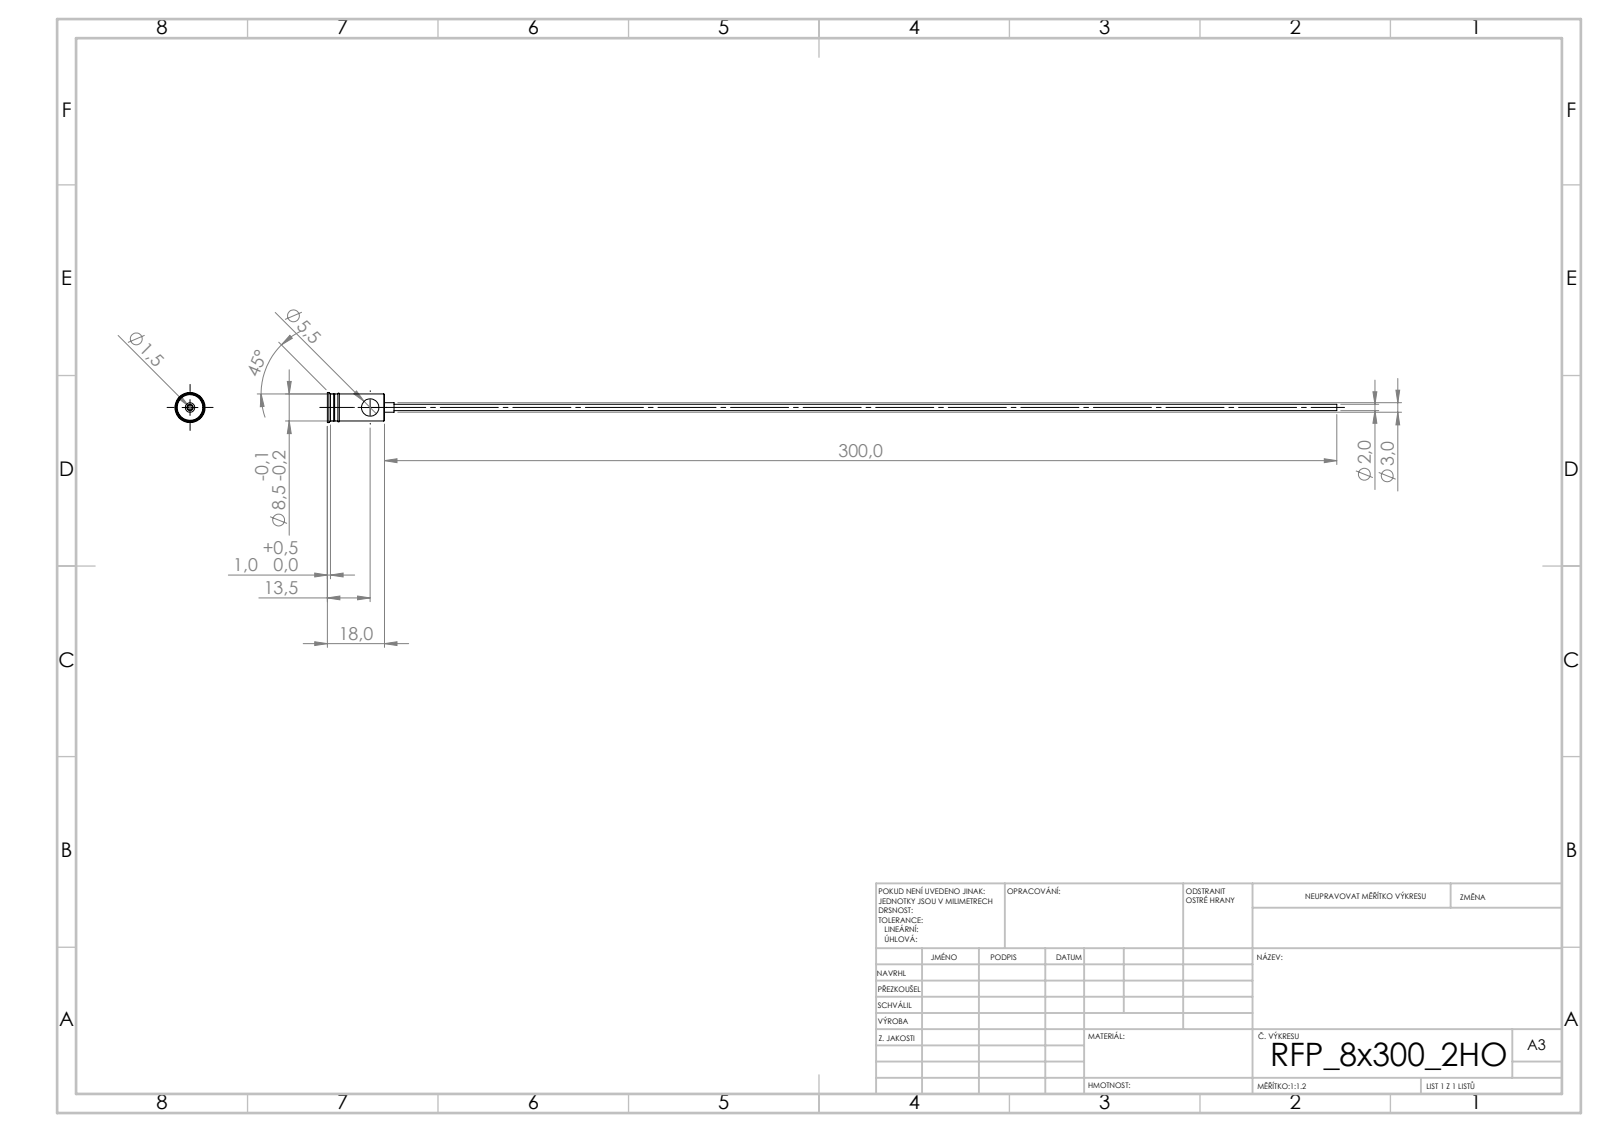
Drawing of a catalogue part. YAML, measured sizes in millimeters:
step_written_by: "SolidWorks 2019 (CONFIG_CONTROL_DESIGN)"
units: millimeters
bodies: {solids: 1, faces: 44, planar: 20, cylindrical: 16, other: 8}
overall_size: [318, 9.5, 9.5]
volume: 1237
surface_area: 4053
round_holes:
  - {diameter: 1.5, count: 1}
  - {diameter: 5.5, count: 1}
round_bosses_or_shafts:
  - {diameter: 9.5, count: 1}
  - {diameter: 8.5, count: 1}
  - {diameter: 3, count: 1}
  - {diameter: 2, count: 1}
face_to_face_distances: [18, 16, 2, 3.9, 15.7, 2.3, 3, 18.7, 19, 21]
